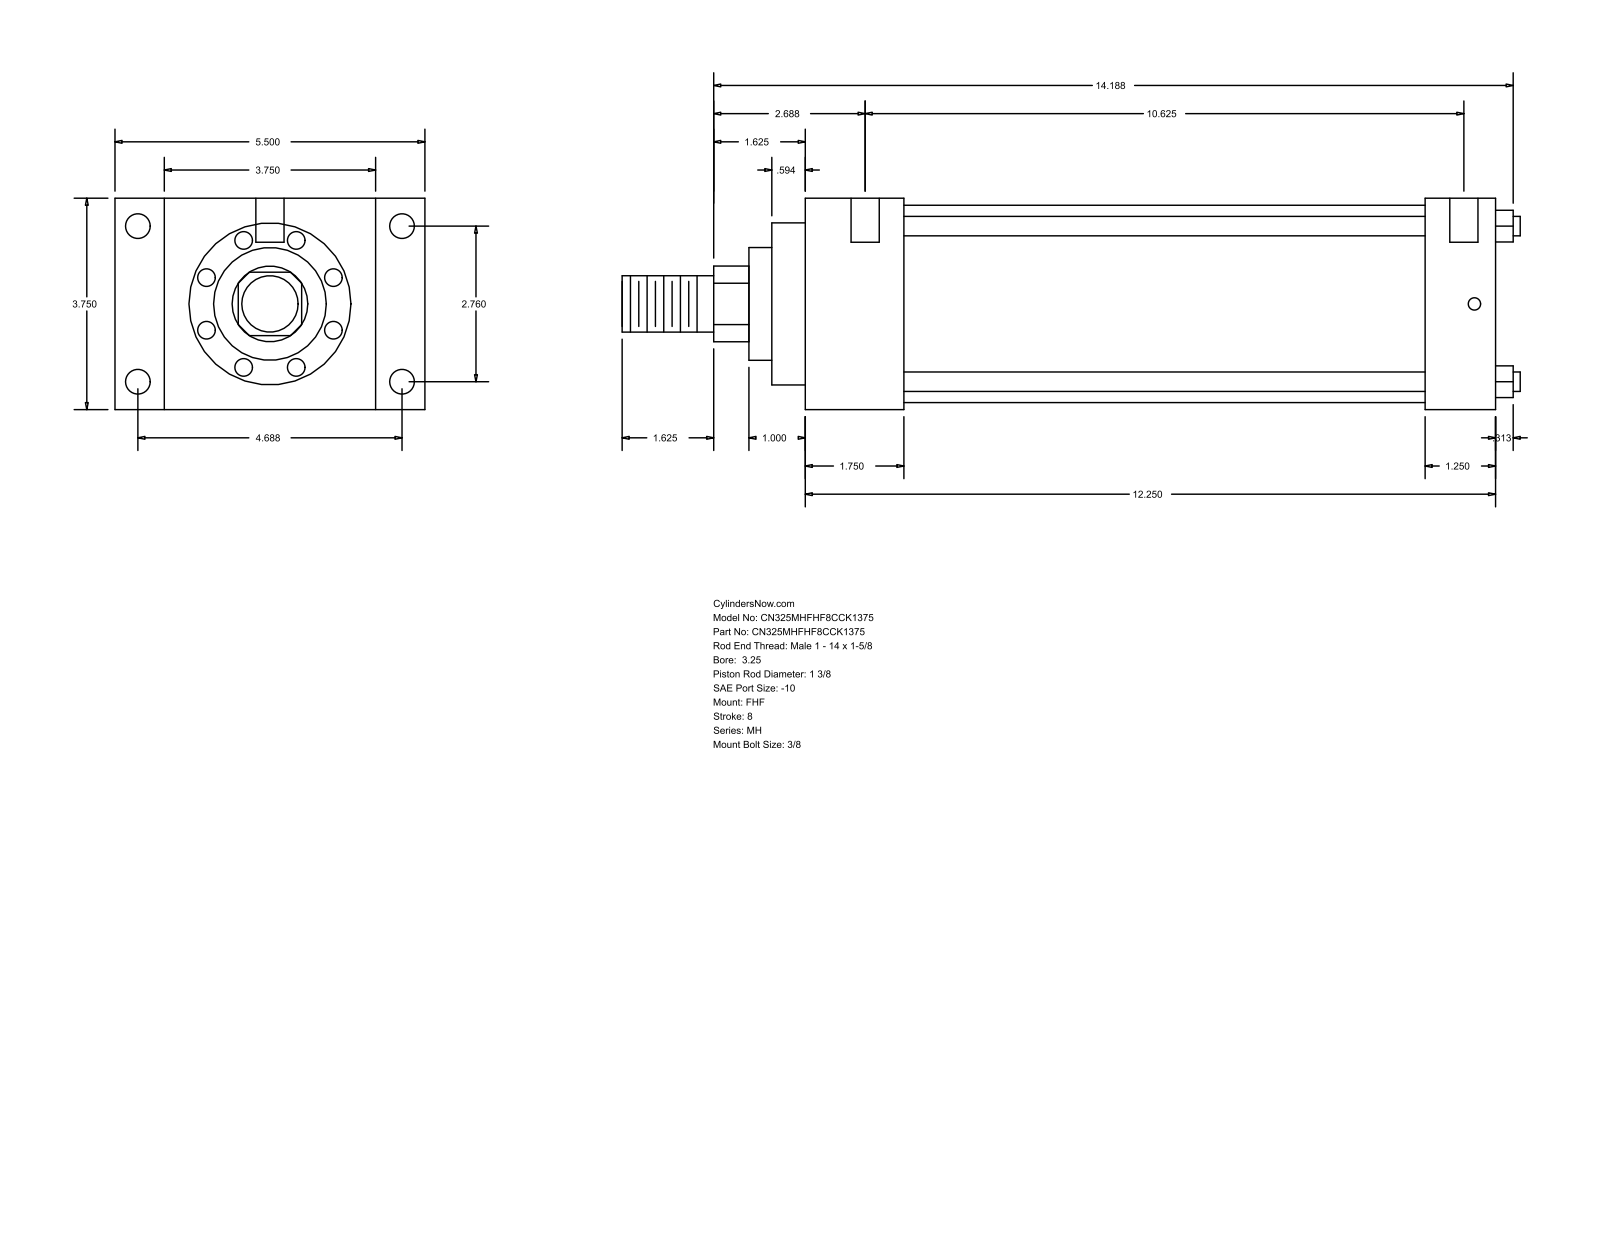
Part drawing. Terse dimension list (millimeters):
name: MH_FHF__0325_1.375
written by: GSSL Pune (CONFIG_CONTROL_DESIGN)
unit: mm
bodies: 0 solids, 90 faces (61 planar, 29 cylindrical, 0 other)
size: 404.81 × 139.7 × 95.25
holes: 4× ⌀5.56, 4× ⌀11.13, 2× ⌀12.7
bosses: 4× ⌀8.76, 1× ⌀88.9, 1× ⌀73.03, 1× ⌀50.8, 1× ⌀34.92, 1× ⌀25.4
rounds: 1× R17.06
face distances: 95.24, 311.16, 44.45, 266.71, 22.23, 117.47, 139.7, 279.41, 234.96, 31.75
hole spacings: 70.1, 119.06, 138.16, 276.23, 1.59, 4.76, 269.88, 271.47
